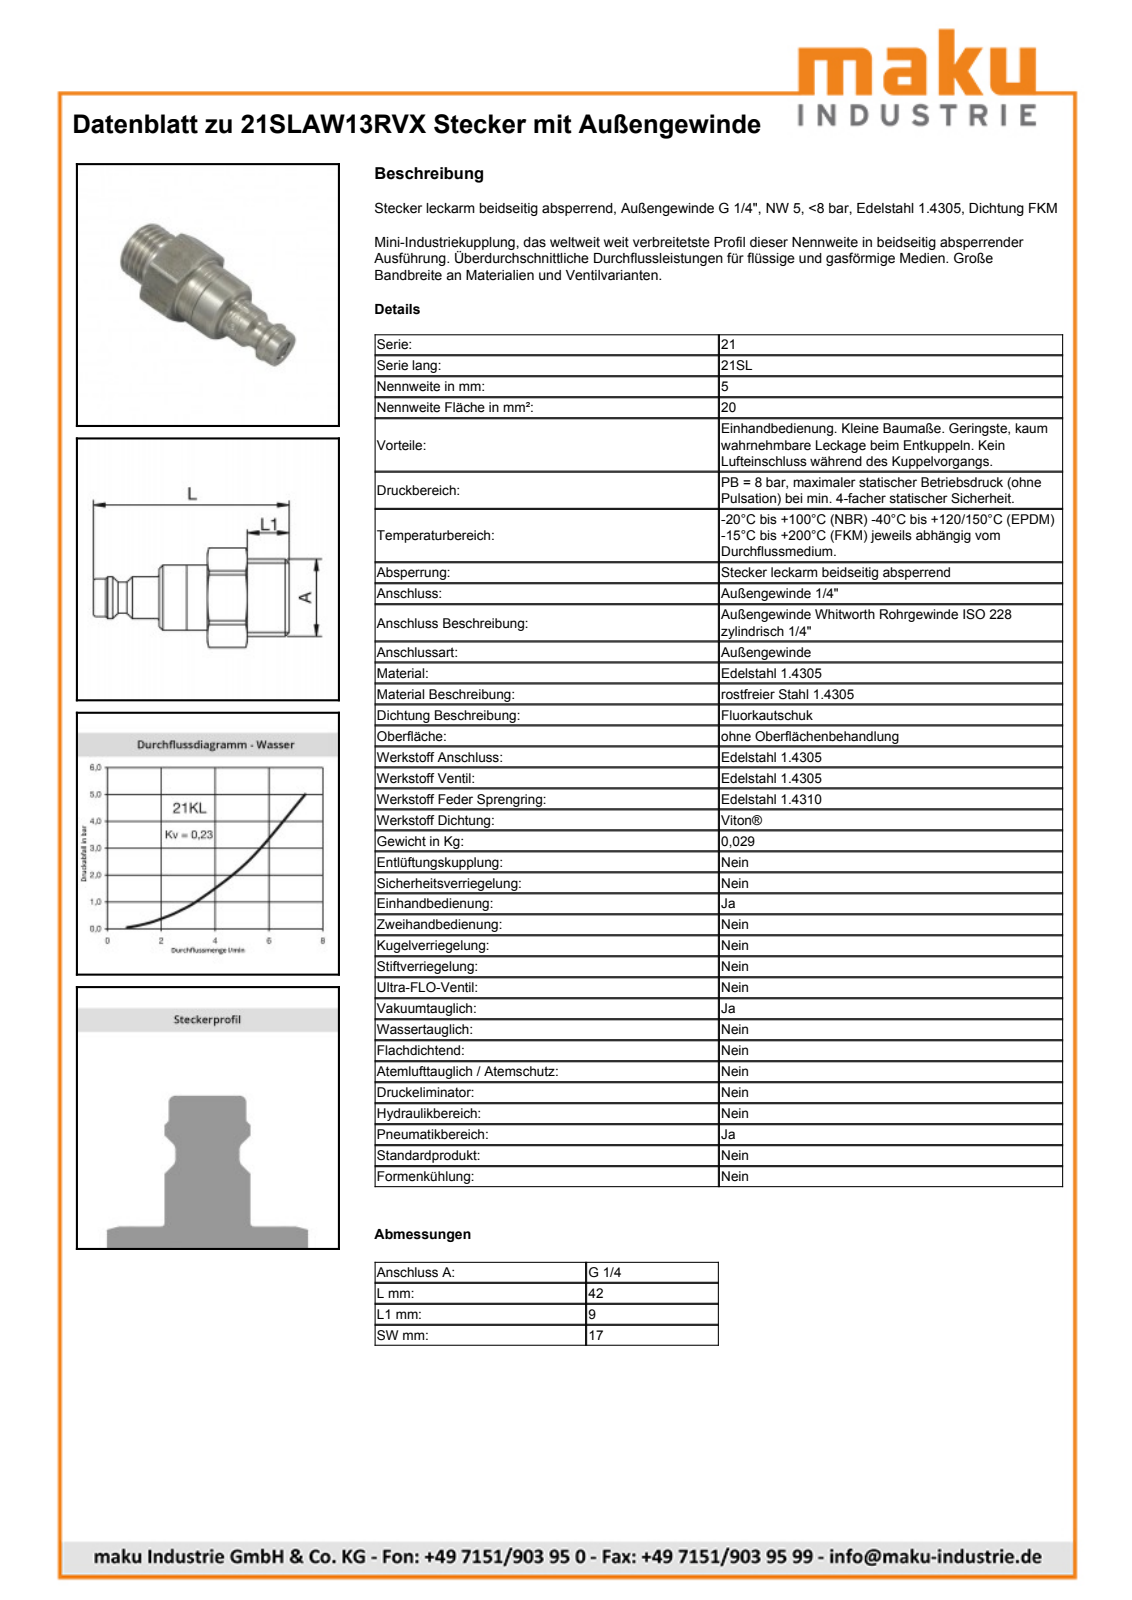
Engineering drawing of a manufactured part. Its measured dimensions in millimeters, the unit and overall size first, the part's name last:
Units: millimetres
Overall size (bounding box): 42 × 18.81 × 18.58
Round bosses / shafts (diameter × count): ⌀14 ×1, ⌀13.8 ×1, ⌀13.16 ×1, ⌀12.49 ×1, ⌀9 ×1, ⌀8.1 ×1, ⌀6.7 ×1
Partial cylindrical surfaces — rounded edges, fillets, slot ends (radius × count): R9.57 ×1
Main face-to-face distances: 17, 9, 8.55, 17.55, 10.35, 18.9, 27.9, 14.1, 24.45, 33
Volume: 5 619 mm³ · Surface area: 2 166 mm²
Bodies: 1 solid, 54 faces (14 planar, 15 cylindrical, 25 other)
Part name (STEP PRODUCT): D107638
STEP written by: Autodesk Inventor 2013 (AUTOMOTIVE_DESIGN)
